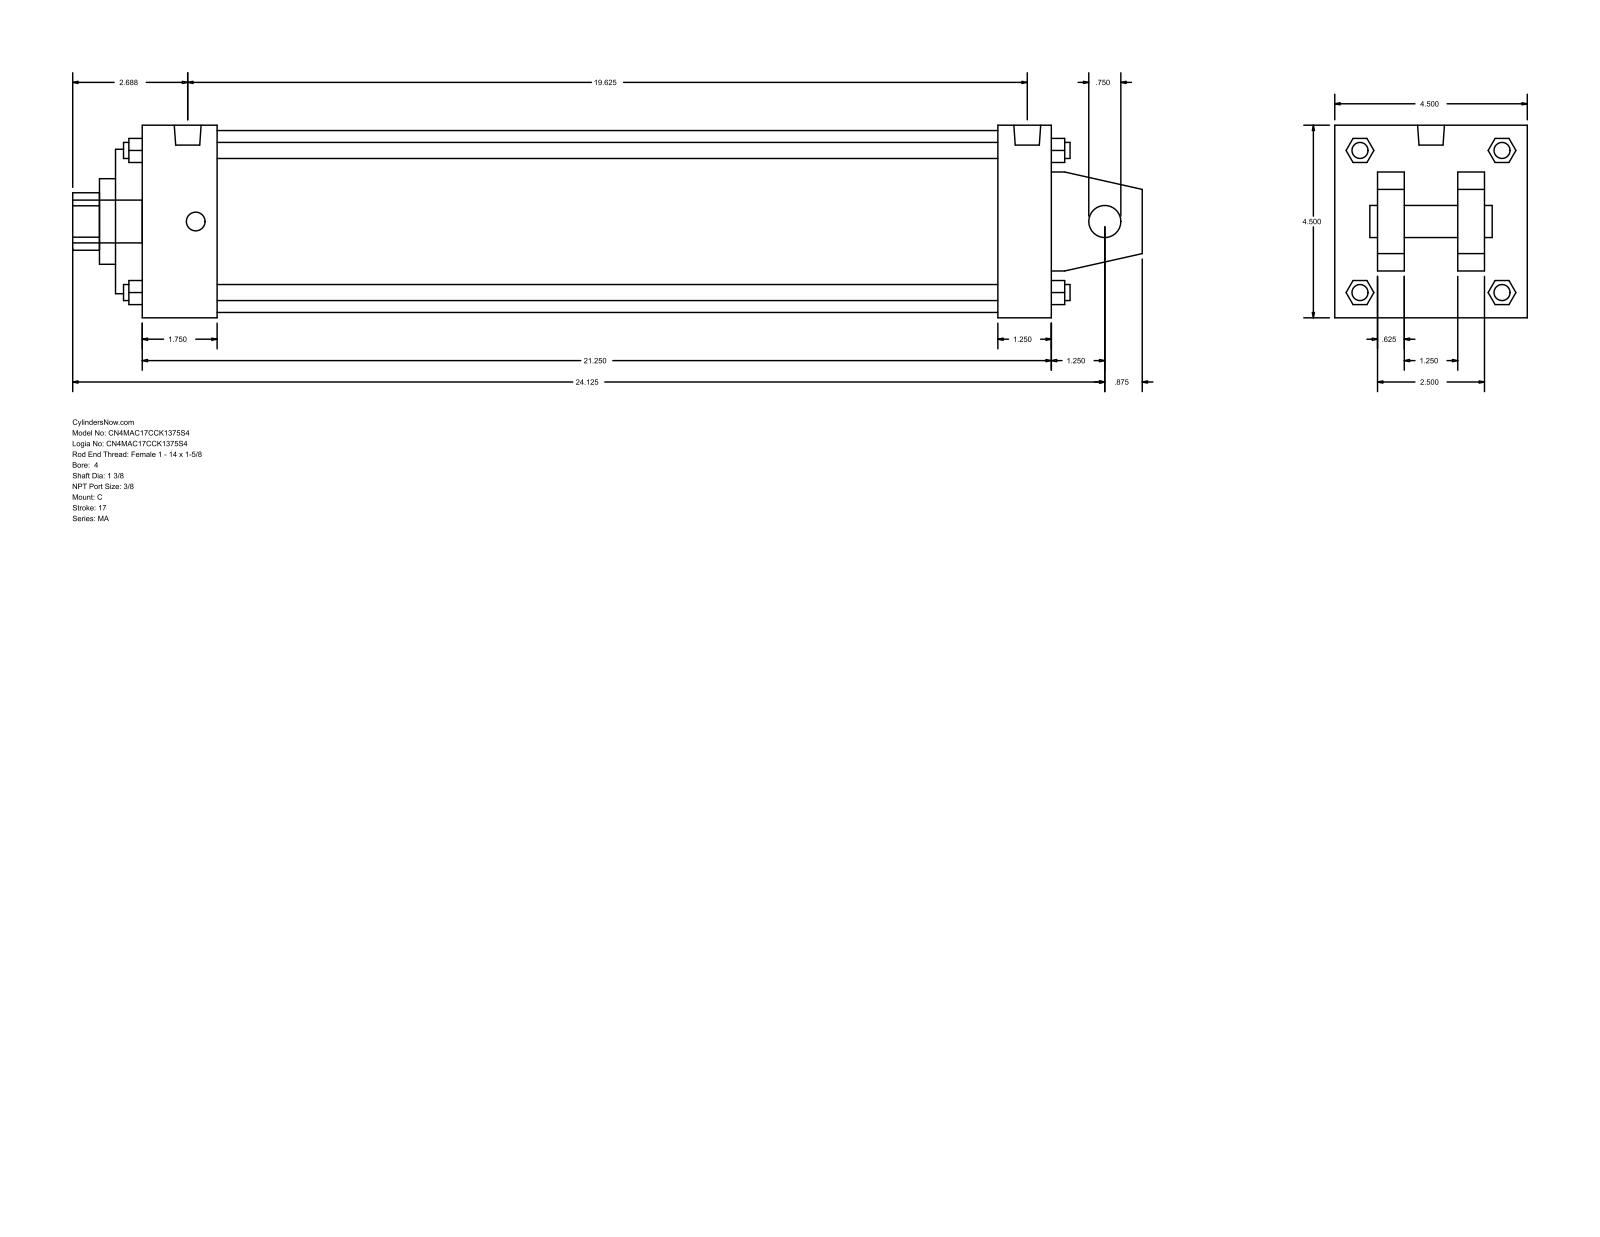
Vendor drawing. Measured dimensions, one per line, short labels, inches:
name: MA_C__0400_1.375
written by: GSSL Pune (CONFIG_CONTROL_DESIGN)
unit: in
bodies: 0 solids, 141 faces (109 planar, 32 cylindrical, 0 other)
size: 25 × 4.5 × 4.5
holes: 1× ⌀0.75, 1× ⌀1.375, 1× ⌀2, 1× ⌀3.375, 1× ⌀4.25
bosses: 4× ⌀0.437, 4× ⌀0.375, 2× ⌀0.627, 1× ⌀1
rounds: 1× R0.672
face distances: 4.5, 0.625, 21.25, 2.875, 1.625, 1, 3.5, 1.875, 21.875, 20.625
